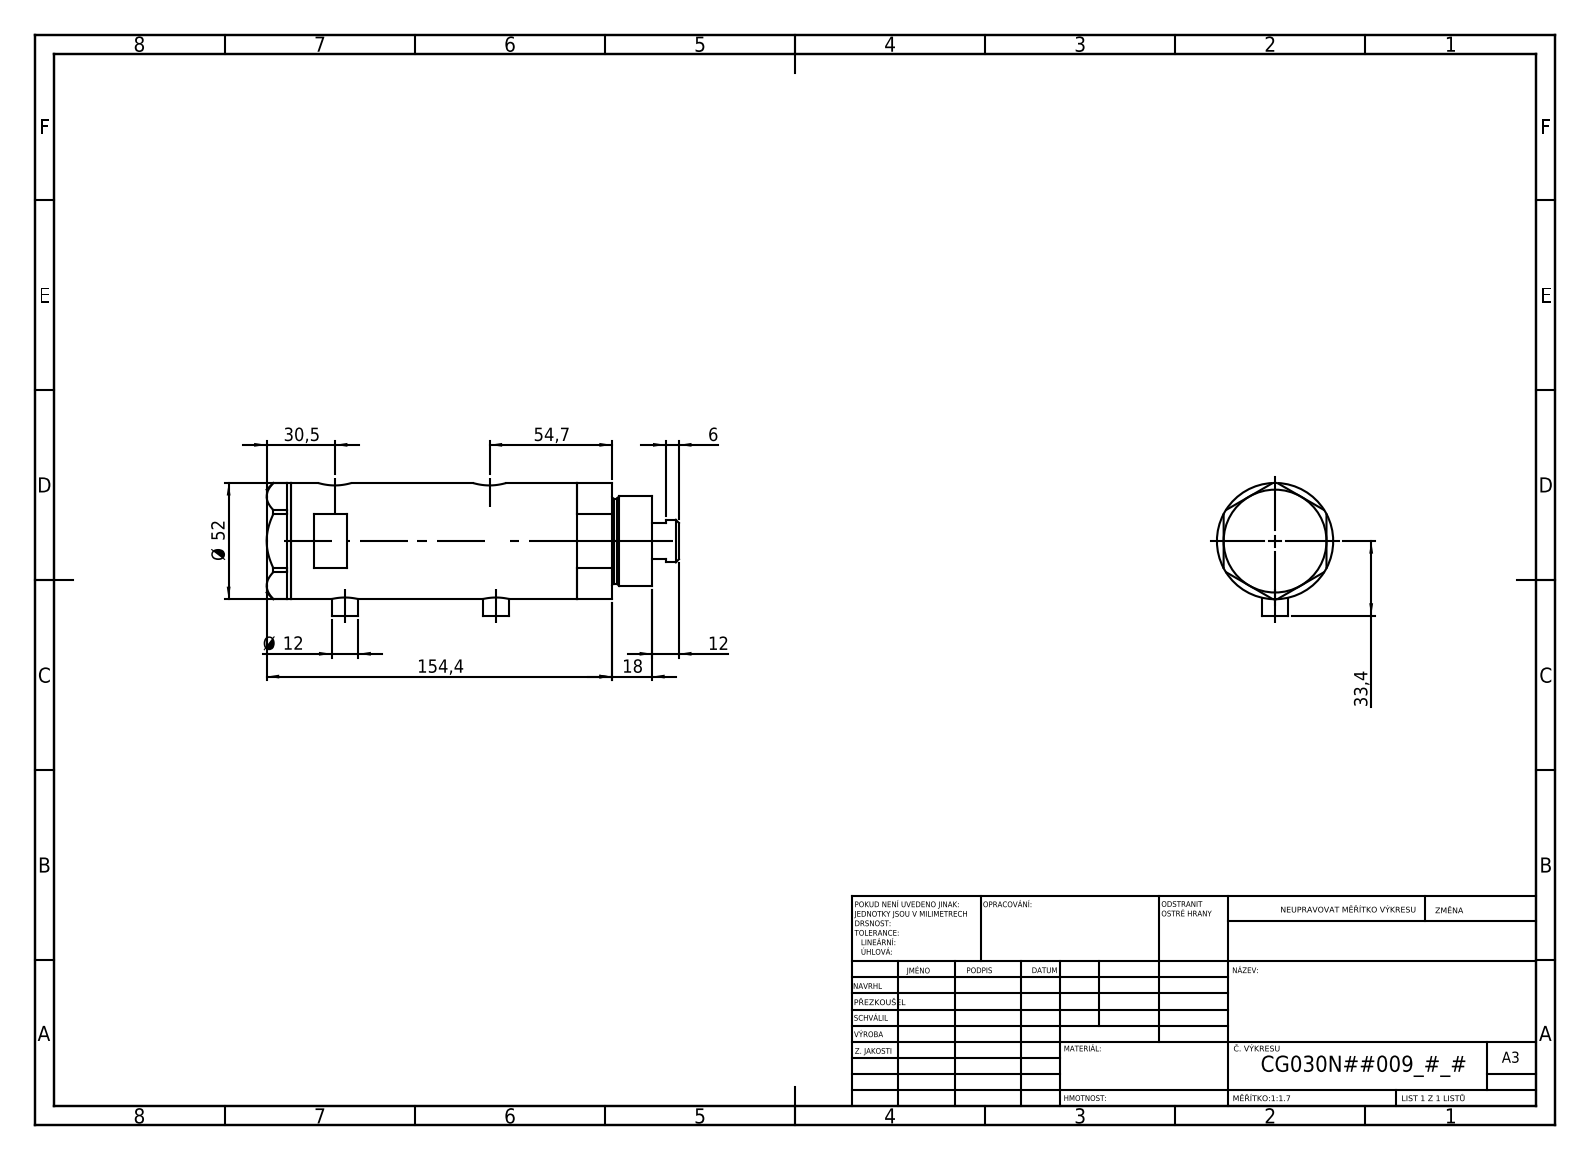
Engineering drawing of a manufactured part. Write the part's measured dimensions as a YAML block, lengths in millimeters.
part_name: "V270CG_MIDDLE; V270CG_BACK; V270CG_FRONT; V270CG_VC"
step_written_by: "SolidWorks 2019 (CONFIG_CONTROL_DESIGN)"
units: millimeters
bodies: {solids: 4, faces: 134, planar: 65, cylindrical: 49, other: 20}
overall_size: [184.4, 59.4, 52]
volume: 343166
surface_area: 77794
round_holes:
  - {diameter: 9.73, count: 2}
  - {diameter: 12.5, count: 2}
  - {diameter: 15, count: 2}
  - {diameter: 6.5, count: 1}
  - {diameter: 20, count: 1}
  - {diameter: 21.5, count: 1}
  - {diameter: 30, count: 1}
  - {diameter: 33, count: 1}
  - {diameter: 44, count: 1}
round_bosses_or_shafts:
  - {diameter: 12, count: 2}
  - {diameter: 52, count: 1}
  - {diameter: 40, count: 1}
  - {diameter: 38, count: 1}
  - {diameter: 19, count: 1}
face_to_face_distances: [91.5, 23.8, 67.7, 11, 34.8, 102.5, 46, 138.9, 127.9, 104.1]
hole_center_spacings: [2.9, 4.5, 64.7, 67.6, 69.2, 72.1]
